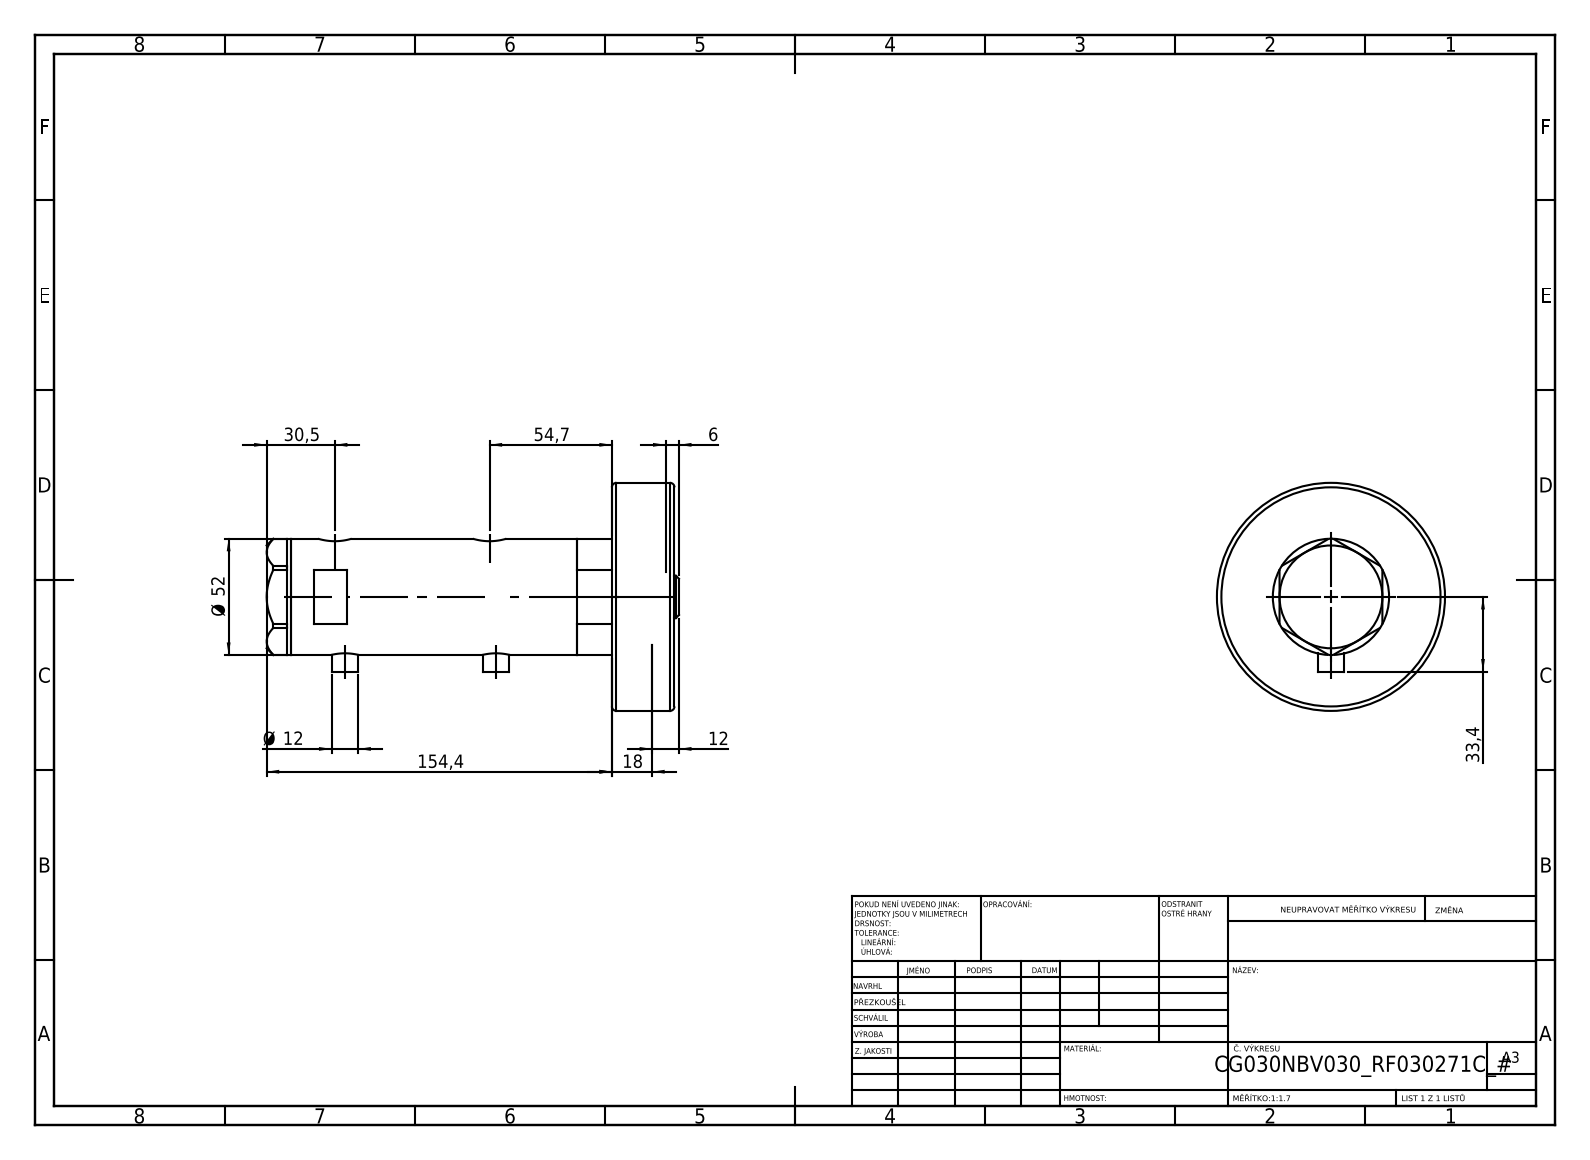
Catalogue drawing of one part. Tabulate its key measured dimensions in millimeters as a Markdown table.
| quantity | value |
| --- | --- |
| part name | V270CG_FRONT; V270CG_BACK; V270CG_271C; V270CG_MIDDLE (+1 more) |
| STEP written by | SolidWorks 2019 (CONFIG_CONTROL_DESIGN) |
| units | millimeters |
| bodies | 5 solids, 144 faces (67 planar, 53 cylindrical, 24 other) |
| overall size | 184.4 × 102 × 102 |
| volume | 527 985 mm³ |
| surface area | 102 901 mm² |
| round holes (diameter × count) | 9.73 × 2, 12.5 × 2, 15 × 2, 6.5 × 1, 20 × 1, 21.5 × 1, 30 × 1, 33 × 1, 40 × 1, 44 × 1 |
| round bosses / shafts (diameter × count) | 12 × 2, 102 × 1, 52 × 1, 38 × 1, 19 × 1 |
| main face-to-face distances | 28, 143.4, 171.4, 91.5, 51.9, 79.9, 23.8, 67.7, 119.6, 147.6 |
| hole center spacings | 2.9, 4.5, 64.7, 67.6, 69.2, 72.1 |
